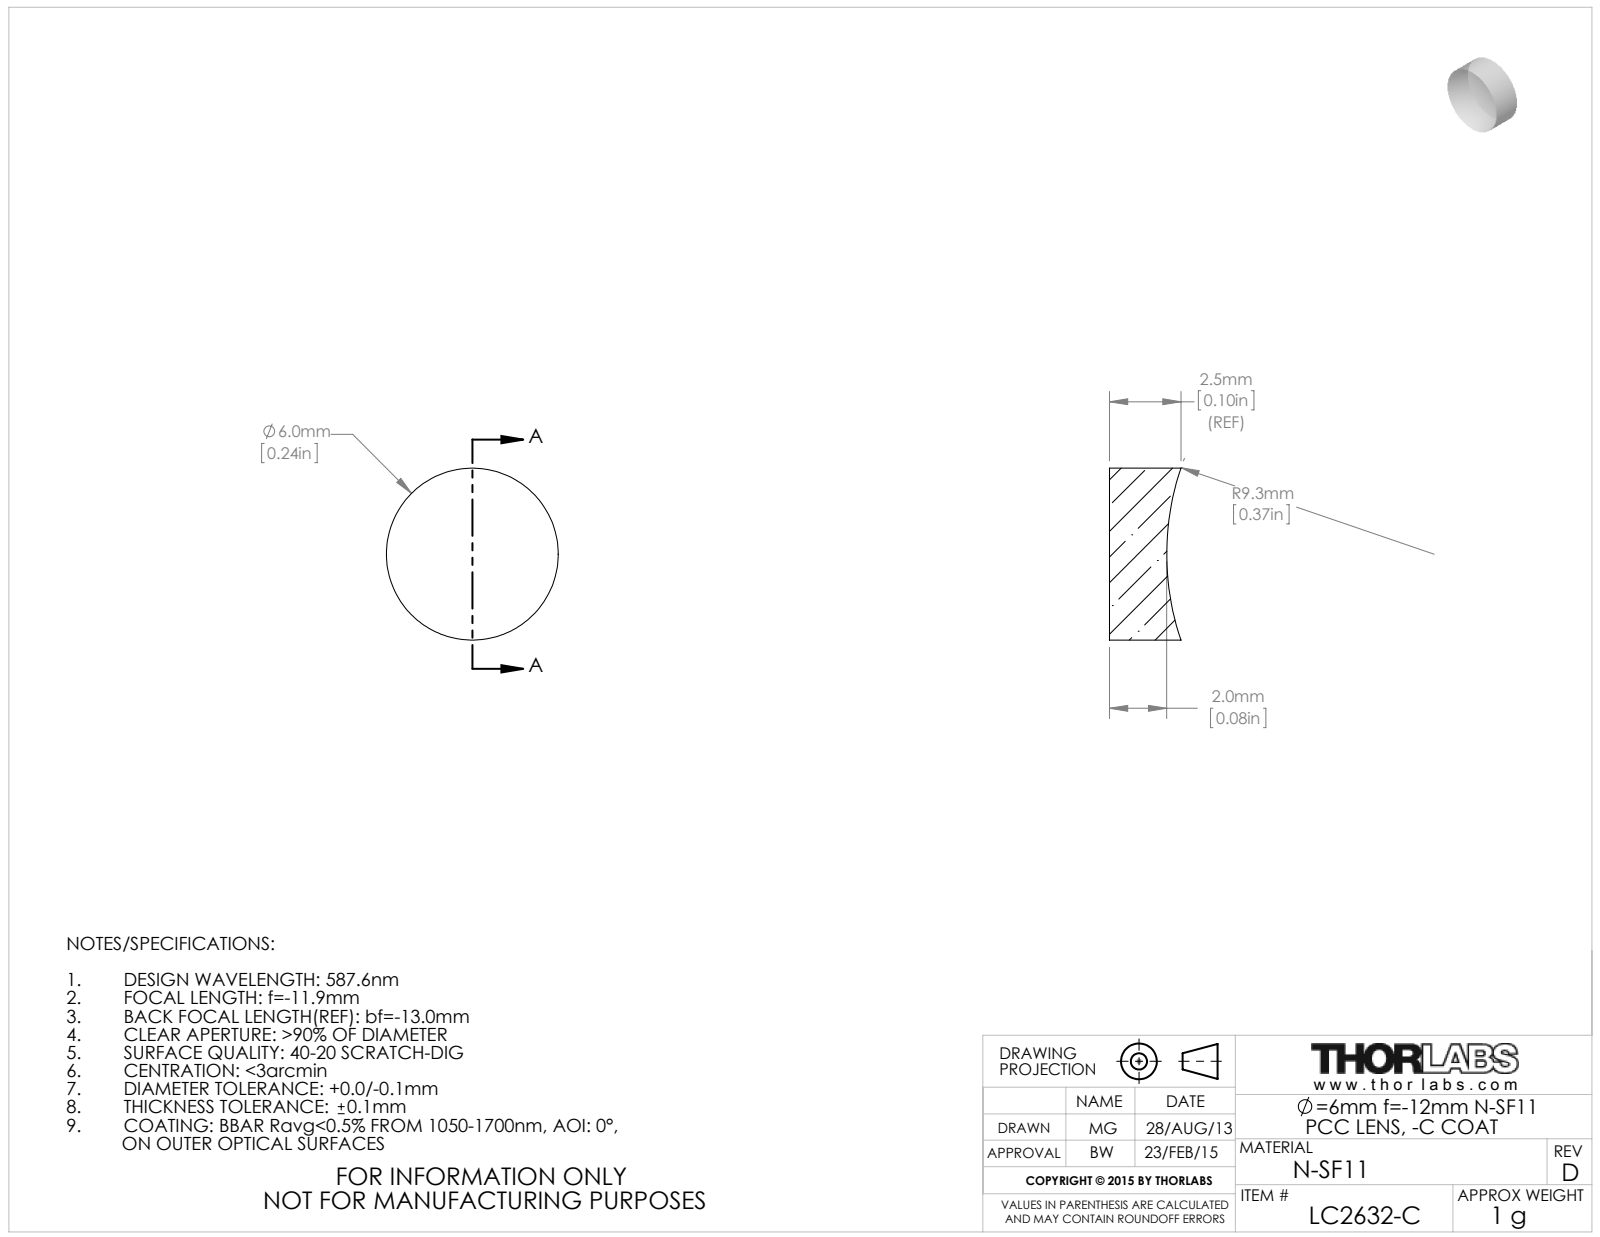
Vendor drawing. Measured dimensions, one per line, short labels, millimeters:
name: 5441-E0W
written by: SolidWorks 2014 (CONFIG_CONTROL_DESIGN)
unit: mm
bodies: 1 solid, 5 faces (1 planar, 2 cylindrical, 2 other)
size: 6 × 6 × 2.5
volume: 63 mm³; area: 104 mm²
bosses: 1× ⌀6
